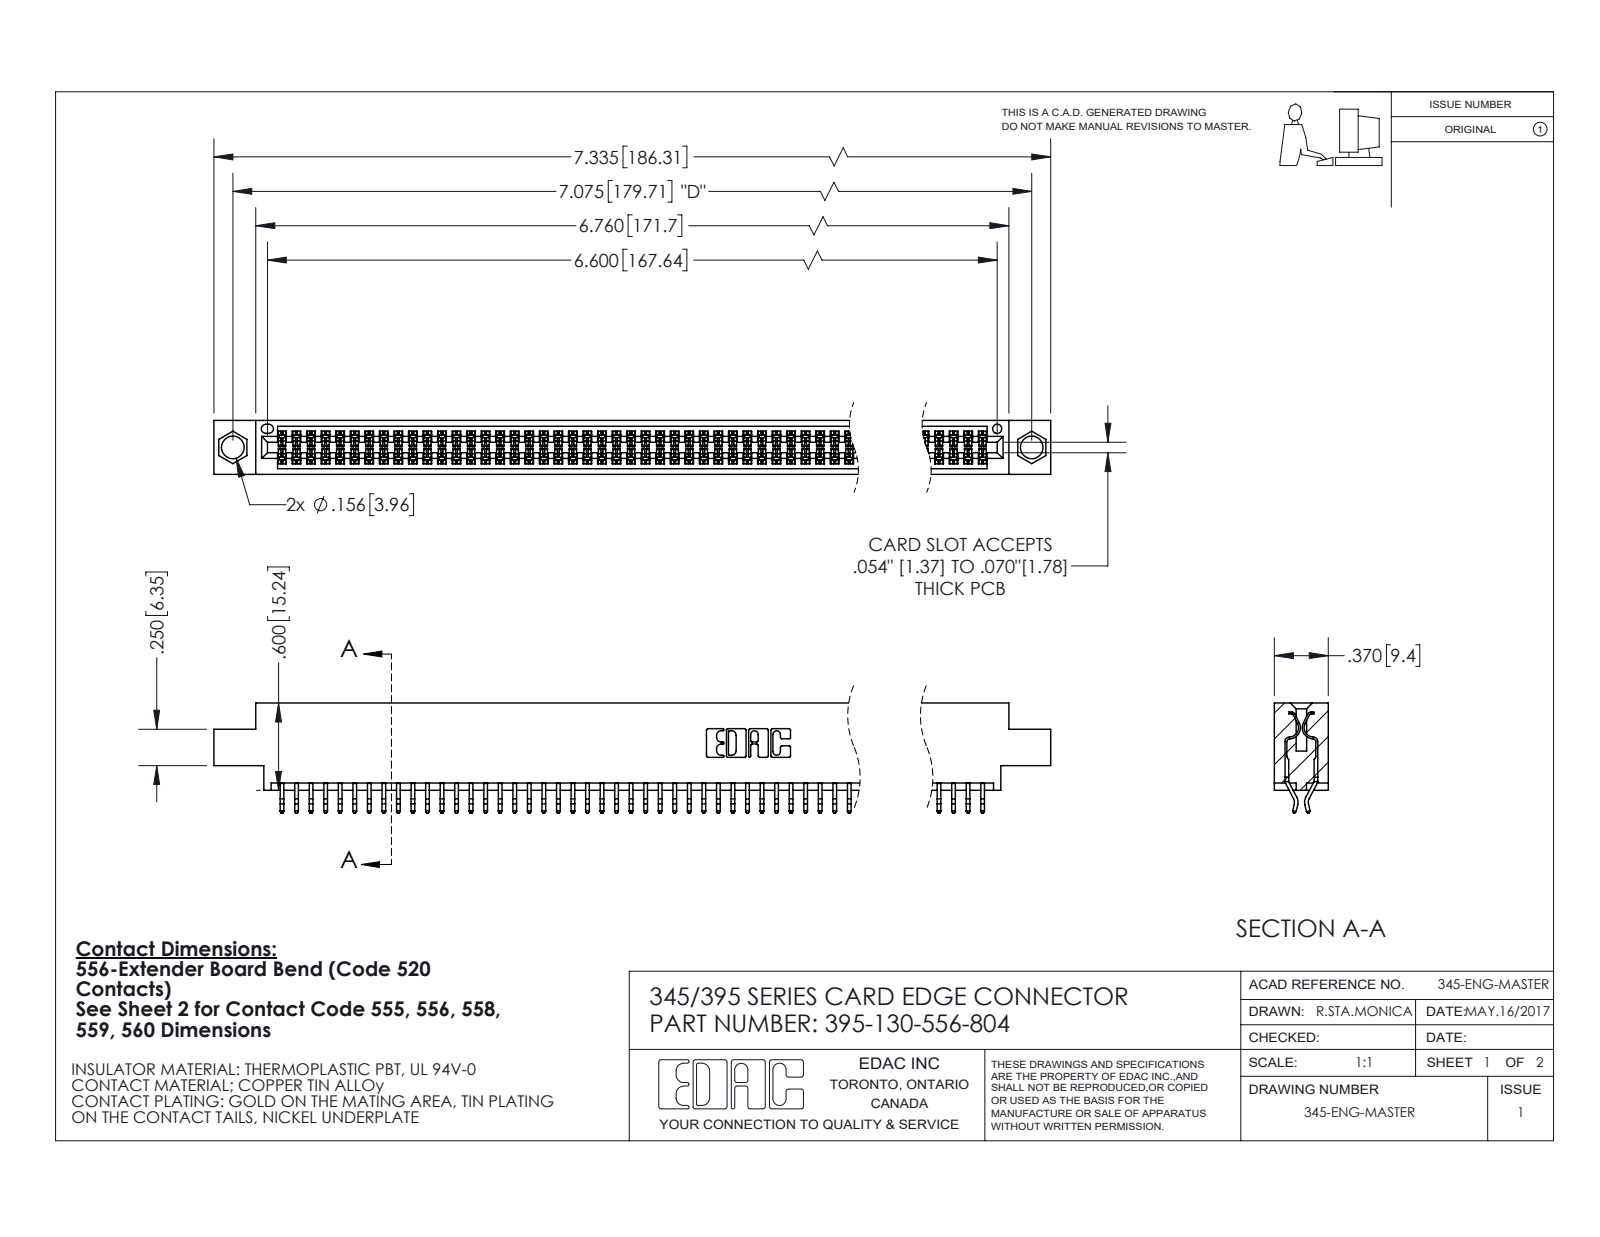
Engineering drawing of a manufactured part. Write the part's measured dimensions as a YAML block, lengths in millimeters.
part_name: "395-130-556-804; 345-292-001_556 Tail; 345 Part_0.170 Offset - 0.156 Dia-TI"
step_written_by: "SolidWorks 2020 (CONFIG_CONTROL_DESIGN)"
units: millimeters
bodies: {solids: 131, faces: 7424, planar: 4908, cylindrical: 2516, other: 0}
overall_size: [186.3, 19.2, 9.4]
volume: 18090
surface_area: 27060
round_holes:
  - {diameter: 4, count: 2}
  - {diameter: 1.6, count: 1}
partial_cylinders:
  - {radius: 0.2, count: 260}
  - {radius: 0.3, count: 22}
  - {radius: 0.2, count: 6}
  - {radius: 0.8, count: 6}
  - {radius: 0.7, count: 3}
  - {radius: 0.3, count: 2}
  - {radius: 0.4, count: 2}
  - {radius: 0.5, count: 2}
face_to_face_distances: [1.8, 7.6, 9.4, 5.1, 0.6, 2.5, 6.9, 5.7, 4.4, 3.8]
hole_center_spacings: [6.9, 173.7, 179.7]
